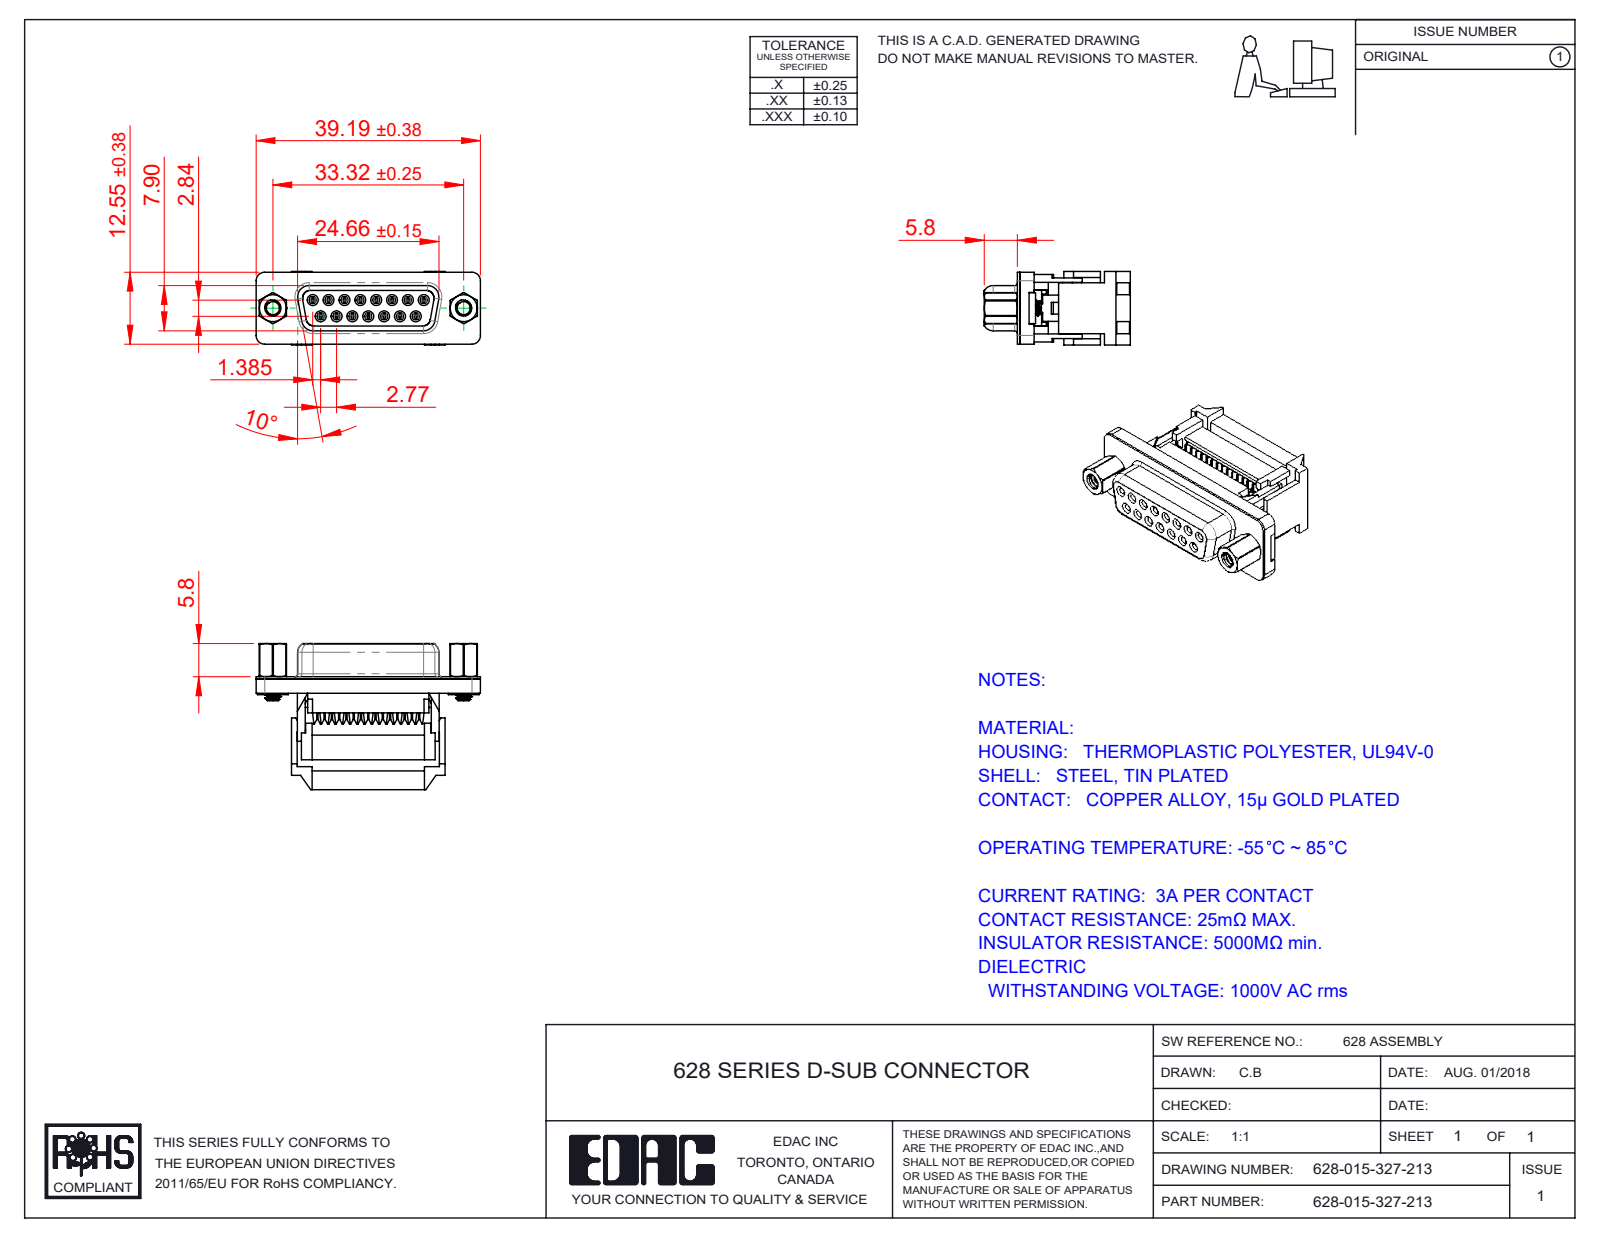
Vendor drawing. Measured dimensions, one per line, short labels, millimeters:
name: 628-015-327-213; 628 IDC Cable Cover_15 Contacts; 628 PB Shell_15 Contacts; 628 4-40 Hex Standoff (+5 more)
written by: SolidWorks 2020 (CONFIG_CONTROL_DESIGN)
unit: mm
bodies: 26 solids, 2755 faces (1610 planar, 629 cylindrical, 516 other)
size: 39.19 × 25.5 × 12.85
volume: 4 542 mm³; area: 9 452 mm²
holes: 15× ⌀1.2, 2× ⌀2.26, 2× ⌀2.29, 2× ⌀4, 2× ⌀4.8, 2× ⌀5
bosses: 2× ⌀4.9, 2× ⌀2.79
rounds: 64× R0.9, 60× R1.2, 34× R0.5, 30× R0.15, 15× R0.64, 15× R0.65, 15× R0.89, 15× R0.94
face distances: 1.9, 0.4, 1.03, 5.2, 1, 7.05, 7.07, 2.33, 0.42, 8.1
hole spacings: 3.16, 2.77, 5.54, 8.31, 5.03, 7.48, 11.08, 5.04
